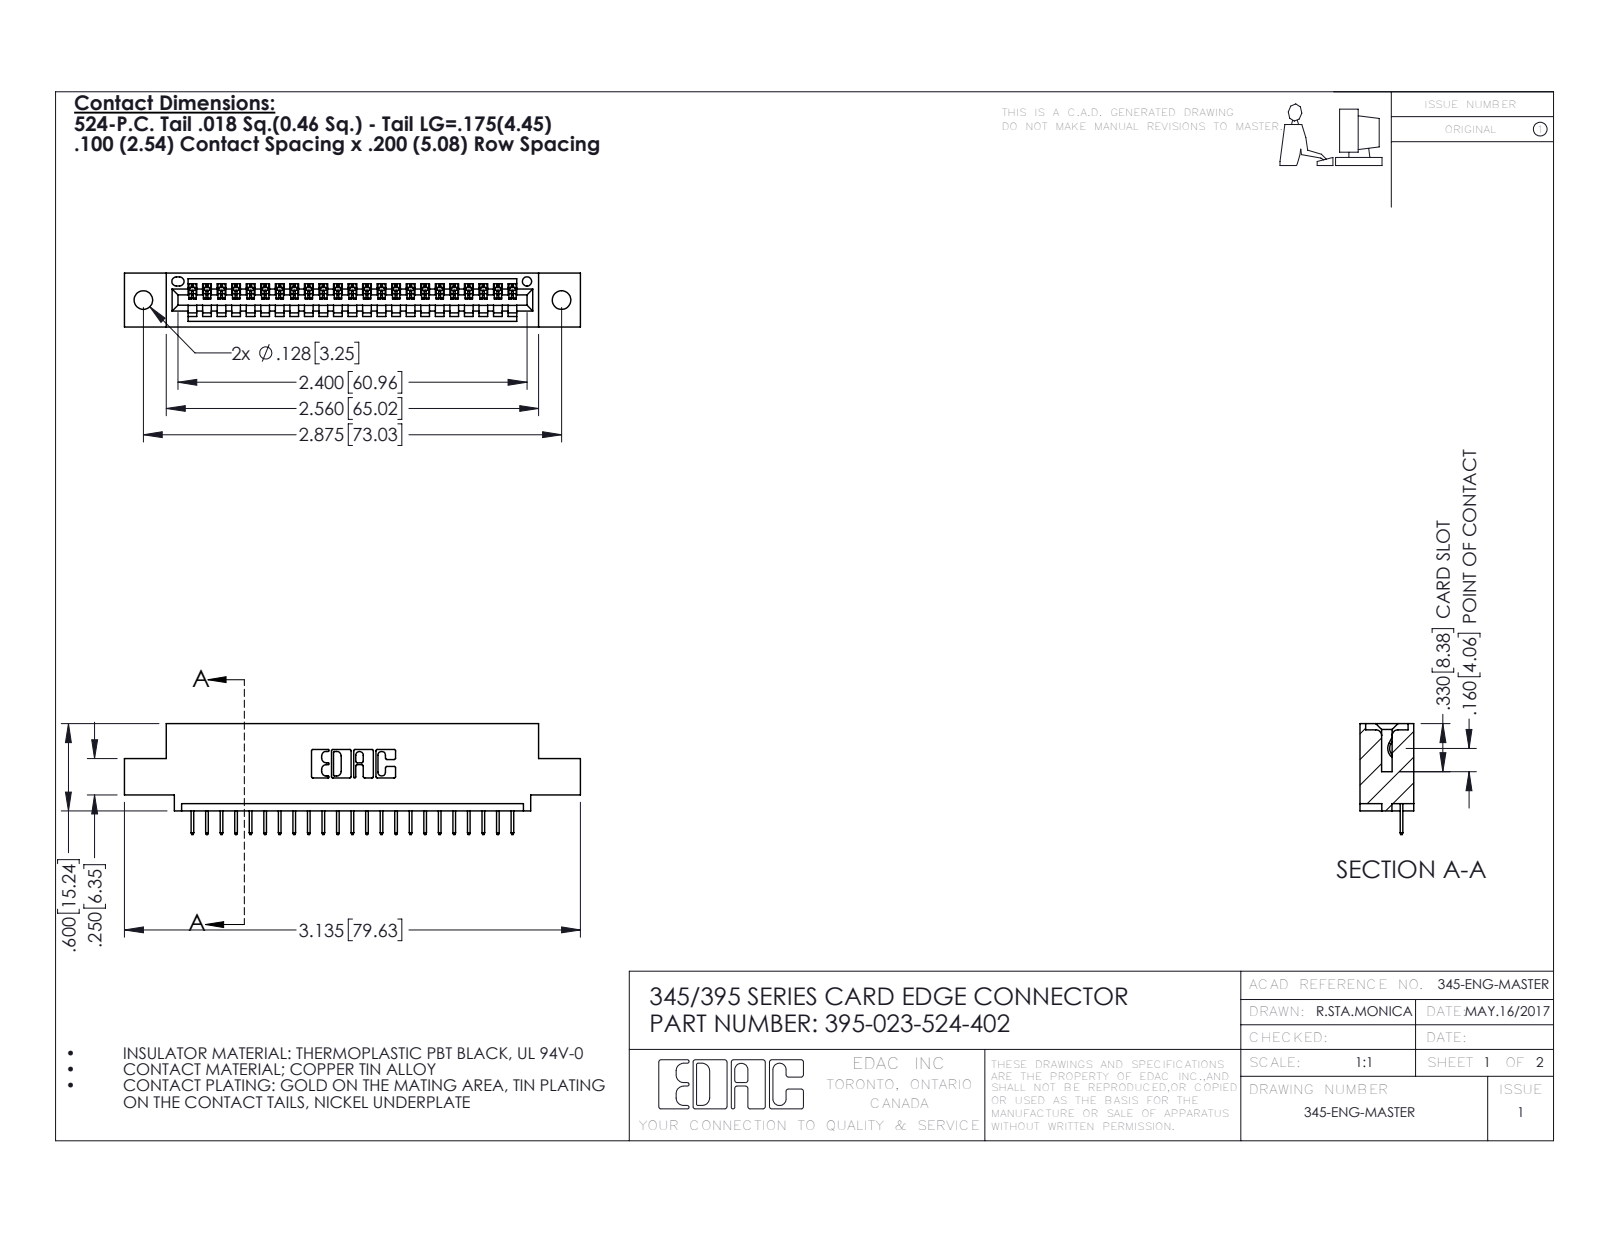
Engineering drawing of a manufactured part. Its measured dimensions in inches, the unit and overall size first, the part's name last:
Units: inches
Overall size (bounding box): 3.135 × 0.762 × 0.37
Round holes (diameter × count): ⌀0.128 ×2, ⌀0.064 ×1
Partial cylindrical surfaces — rounded edges, fillets, slot ends (radius × count): R0.006 ×46, R0.01 ×22, R0.007 ×6, R0.031 ×6, R0.026 ×3, R0.031 ×2, R0.04 ×2, R0.014 ×1
Main face-to-face distances: 0.072, 0.298, 0.37, 0.2, 0.098, 0.272, 0.025, 0.225, 0.072, 0.149
Hole centre spacings: 0.27, 2.641, 2.875
Volume: 0.44 in³ · Surface area: 13.7 in²
Bodies: 24 solids, 1556 faces (1142 planar, 414 cylindrical, 0 other)
Part name (STEP PRODUCT): 395-023-524-402; 345-292-001_345-293-124; 345 Part_0.110 Offset - 0.128 Dia
STEP written by: SolidWorks 2016 (CONFIG_CONTROL_DESIGN)
